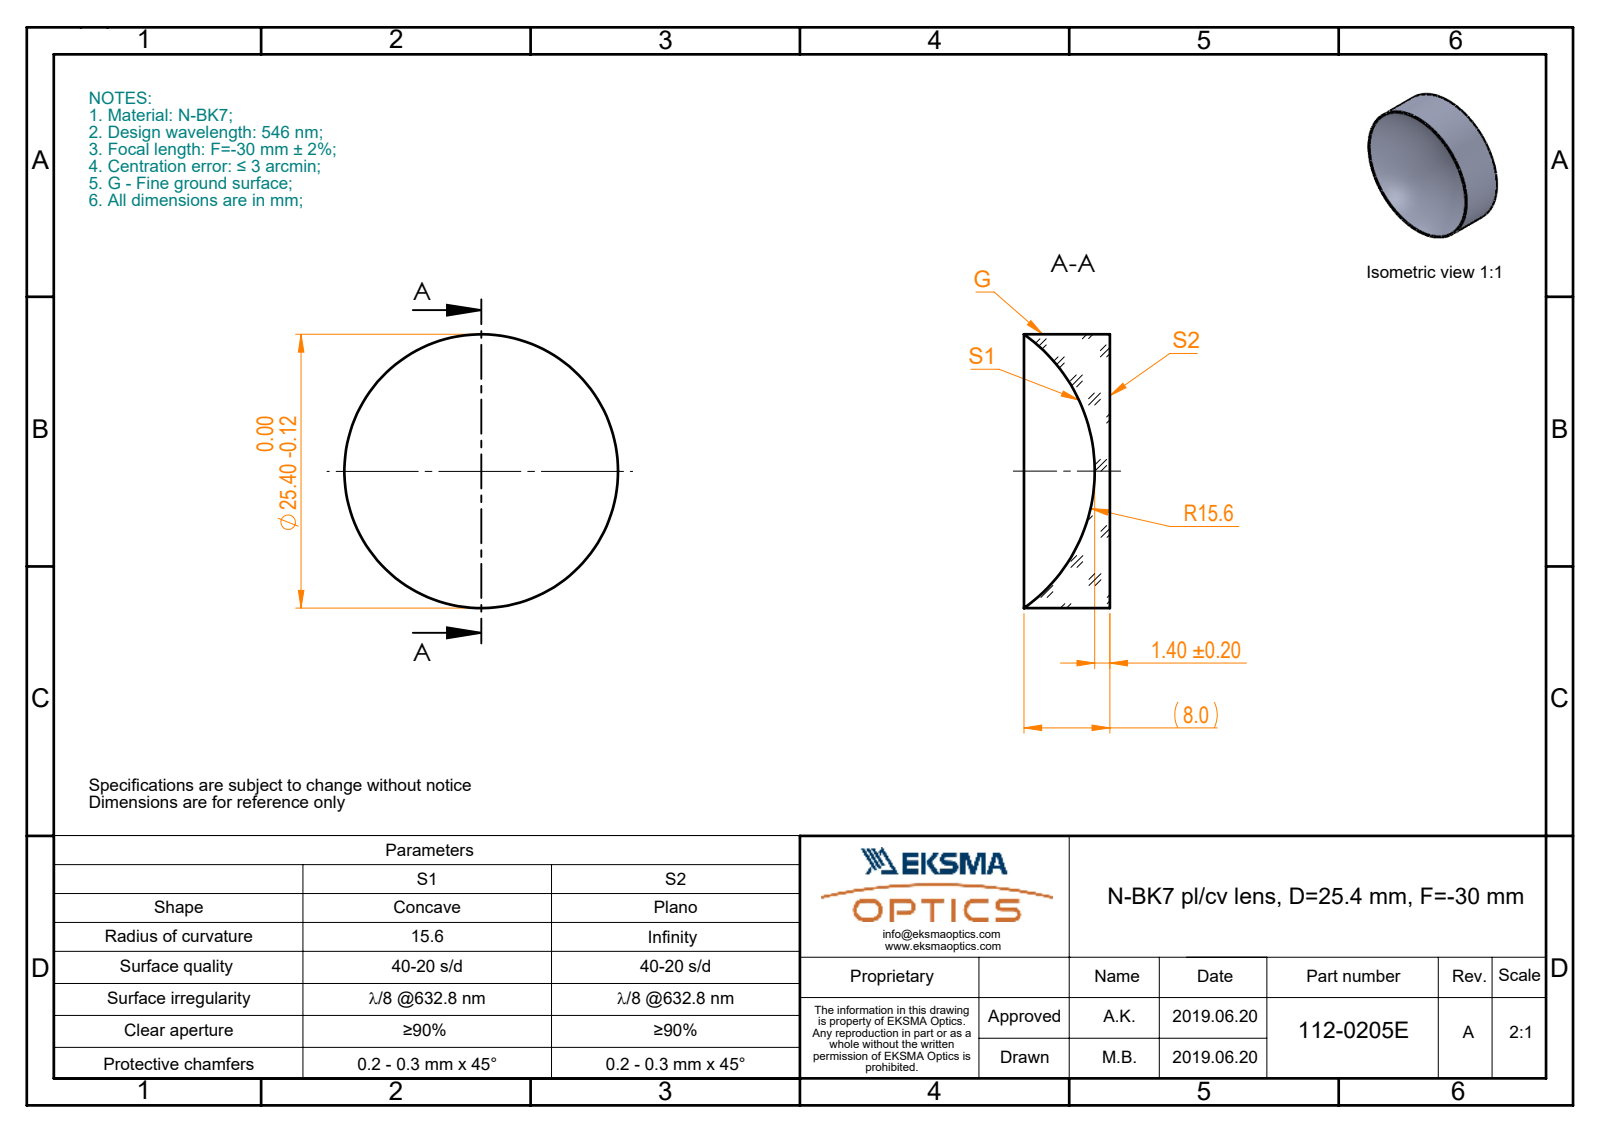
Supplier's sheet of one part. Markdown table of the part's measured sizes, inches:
| quantity | value |
| --- | --- |
| part name | 112-0205E BK7 pl-cv 25.4 F-30 |
| STEP written by | SolidWorks 2017 (CONFIG_CONTROL_DESIGN) |
| units | inches |
| bodies | 1 solid, 5 faces (1 planar, 2 cylindrical, 2 other) |
| overall size | 1 × 1 × 0.314 |
| volume | 0.136 in³ |
| surface area | 2.767 in² |
| round bosses / shafts (diameter × count) | 1 × 1 |
